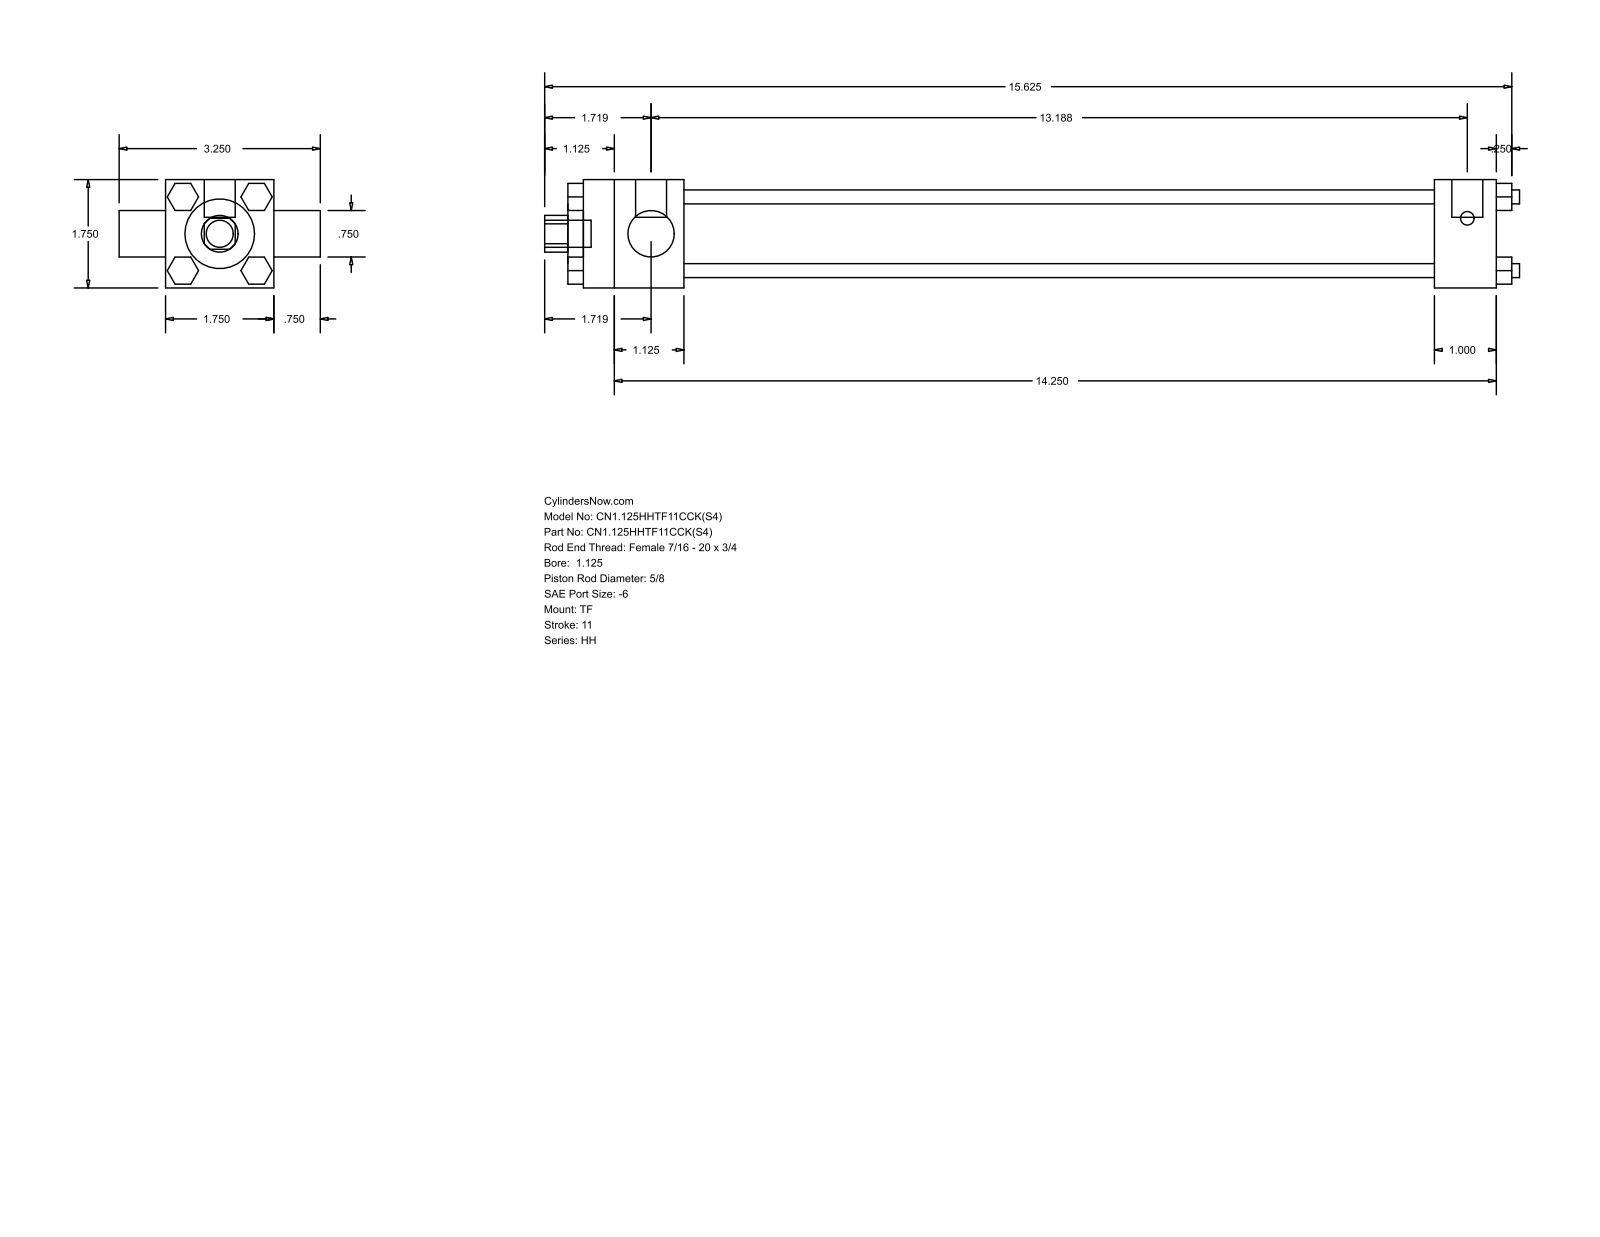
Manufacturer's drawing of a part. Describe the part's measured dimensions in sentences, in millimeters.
The part is named "HH_TF__0112_0.625". Its 3-D file was written by "GSSL Pune (CONFIG_CONTROL_DESIGN)". It is 0 solids with 120 faces: 92 planar, 28 cylindrical and 0 other. Overall it measures 400.05 by 82.55 by 44.45 millimeters. Round holes: 1 of diameter 15.88, 1 of diameter 19.05, 1 of diameter 28.57, 1 of diameter 34.92. Round bosses or shafts: 4 of diameter 5.71, 3 of diameter 5.56, 2 of diameter 12.7, 1 of diameter 11.11. Partial cylindrical surfaces (rounded edges, fillets, slot ends): 1 of radius 7.54. The main face-to-face distances are 44.46, 11.11, 307.97, 333.37, 25.4, 41.27, 349.24, 374.64, 47.62, 6.35.
